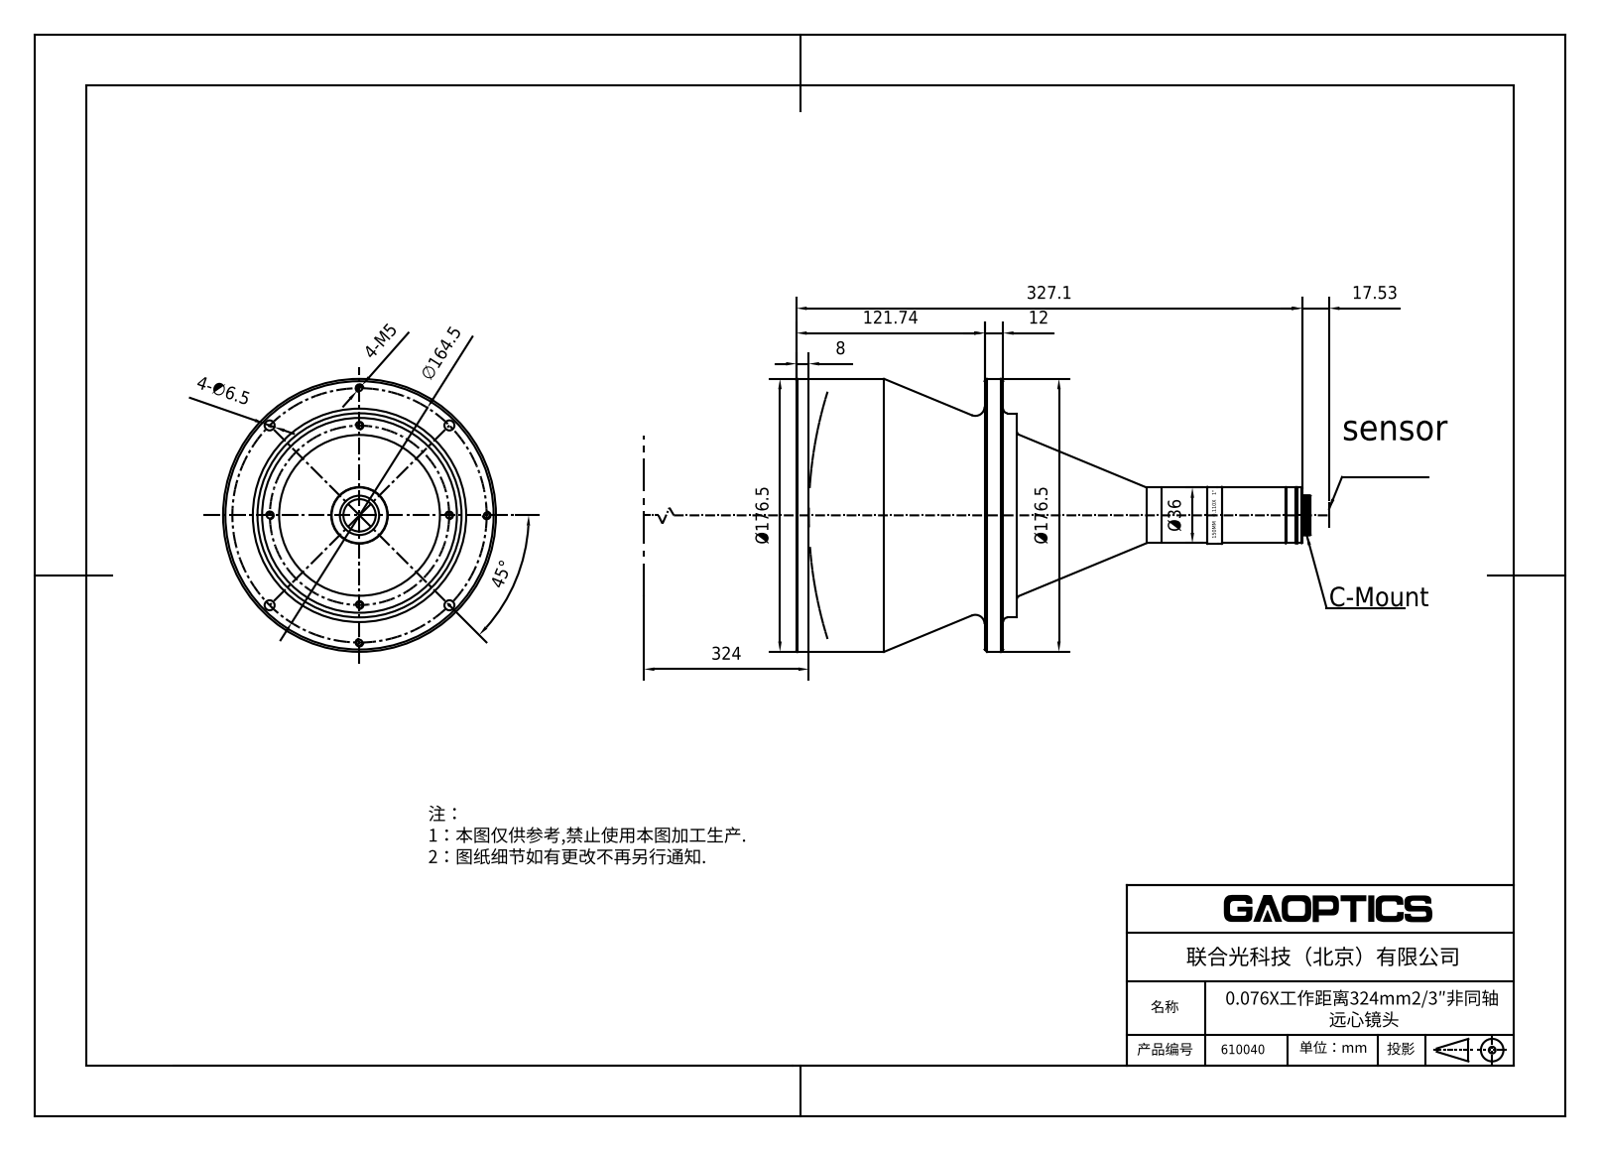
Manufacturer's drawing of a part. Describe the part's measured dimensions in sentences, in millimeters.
The part is named "610041". Its 3-D file was written by "SolidWorks 2016 (AUTOMOTIVE_DESIGN)". It is 0 solids with 242 faces: 31 planar, 108 cylindrical and 103 other. Overall it measures 332.63 by 176.5 by 176.5 millimeters. Round holes: 3 of diameter 2.2, 3 of diameter 3, 1 of diameter 20.9, 1 of diameter 21.8, 1 of diameter 24.6, 1 of diameter 25.8, 1 of diameter 33, 1 of diameter 35. Round bosses or shafts: 1 of diameter 176.5, 1 of diameter 132, 1 of diameter 36.6, 1 of diameter 36, 1 of diameter 32.8, 1 of diameter 31.8, 1 of diameter 31.6, 1 of diameter 29.4. Partial cylindrical surfaces (rounded edges, fillets, slot ends): 2 of radius 0.5. The main face-to-face distances are 133.74, 121.74, 12, 142.74, 21, 9, 324.13, 202.39, 190.39, 181.39. The hole center spacings are 14.7, 25.46.
